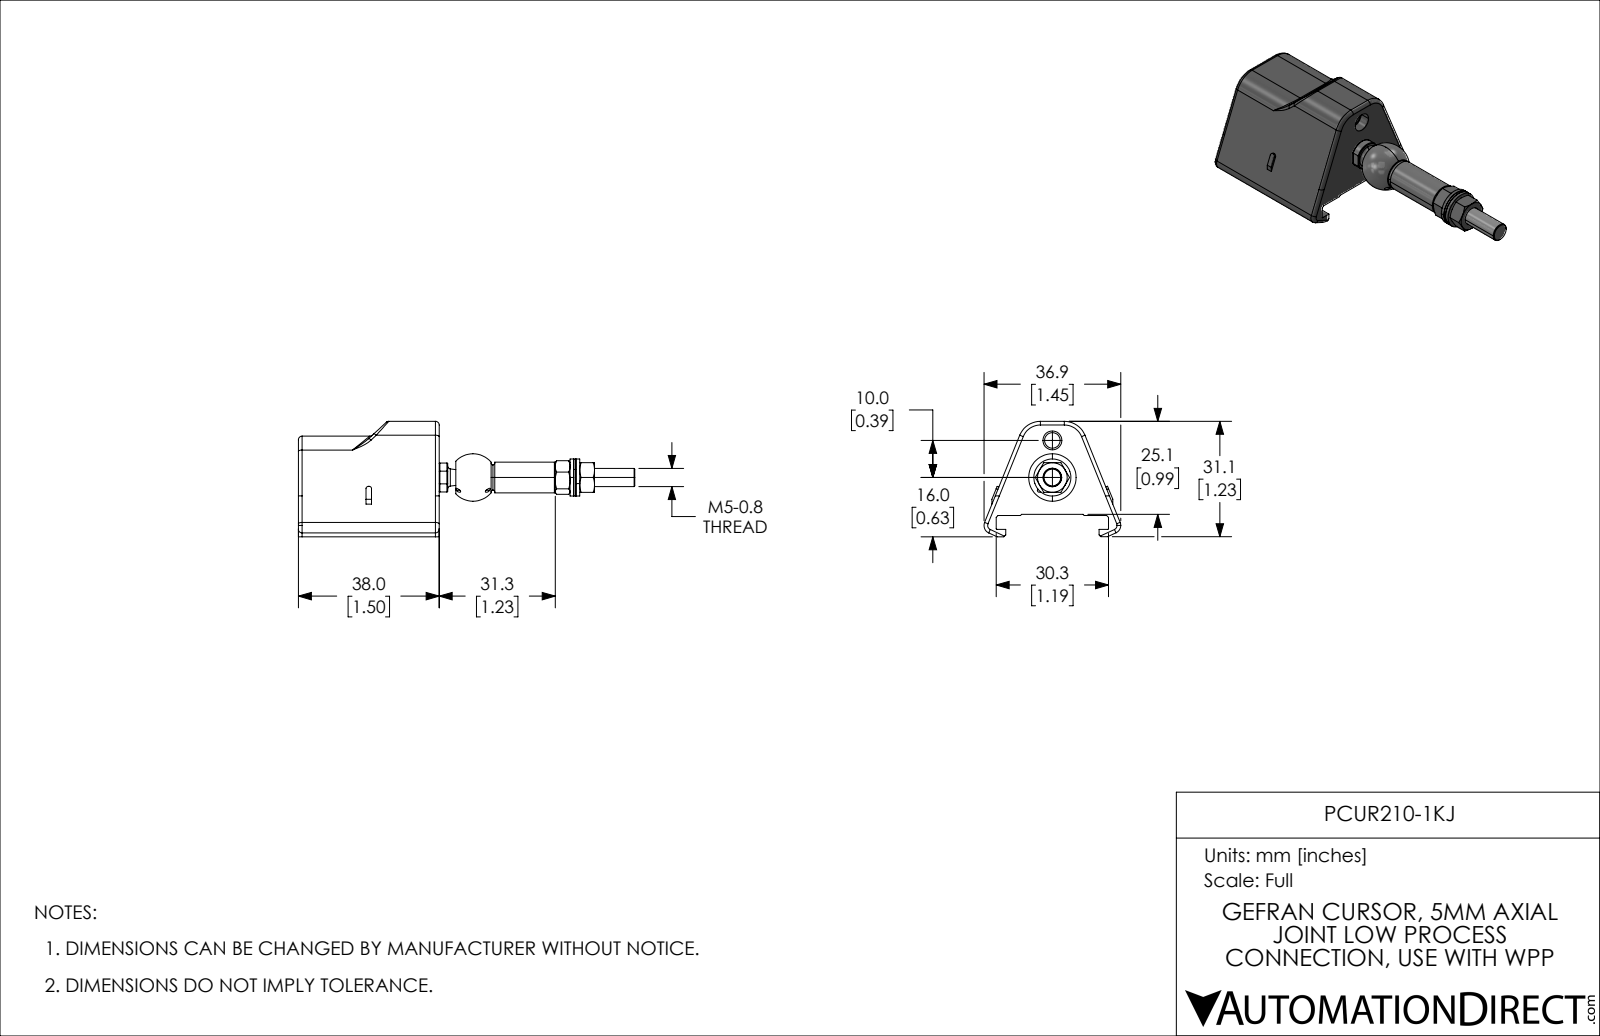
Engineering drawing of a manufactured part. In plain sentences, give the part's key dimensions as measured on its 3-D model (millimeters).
The part is named "PCUR210-1KJ". Its 3-D file was written by "SolidWorks 2021 (CONFIG_CONTROL_DESIGN)". It is 9 solids with 274 faces: 97 planar, 89 cylindrical and 88 other. Overall it measures 90.8 by 36.91 by 31.15 millimeters. Its volume is 24 787 cubic millimeters and its surface area 10 698 square millimeters. Round holes: 2 of diameter 4.2, 2 of diameter 5.1, 1 of diameter 1.1, 1 of diameter 5, 1 of diameter 5.3. Round bosses or shafts: 1 of diameter 10, 1 of diameter 8.3, 1 of diameter 4.89. Partial cylindrical surfaces (rounded edges, fillets, slot ends): 14 of radius 1, 8 of radius 0.45, 6 of radius 0.2, 4 of radius 0.7, 4 of radius 6, 2 of radius 2.2, 1 of radius 3.9. The main face-to-face distances are 38, 12, 13, 25, 9.15, 21.15, 5.75, 2, 1, 3.75. The hole center spacings are 4.91, 10, 13.9.
